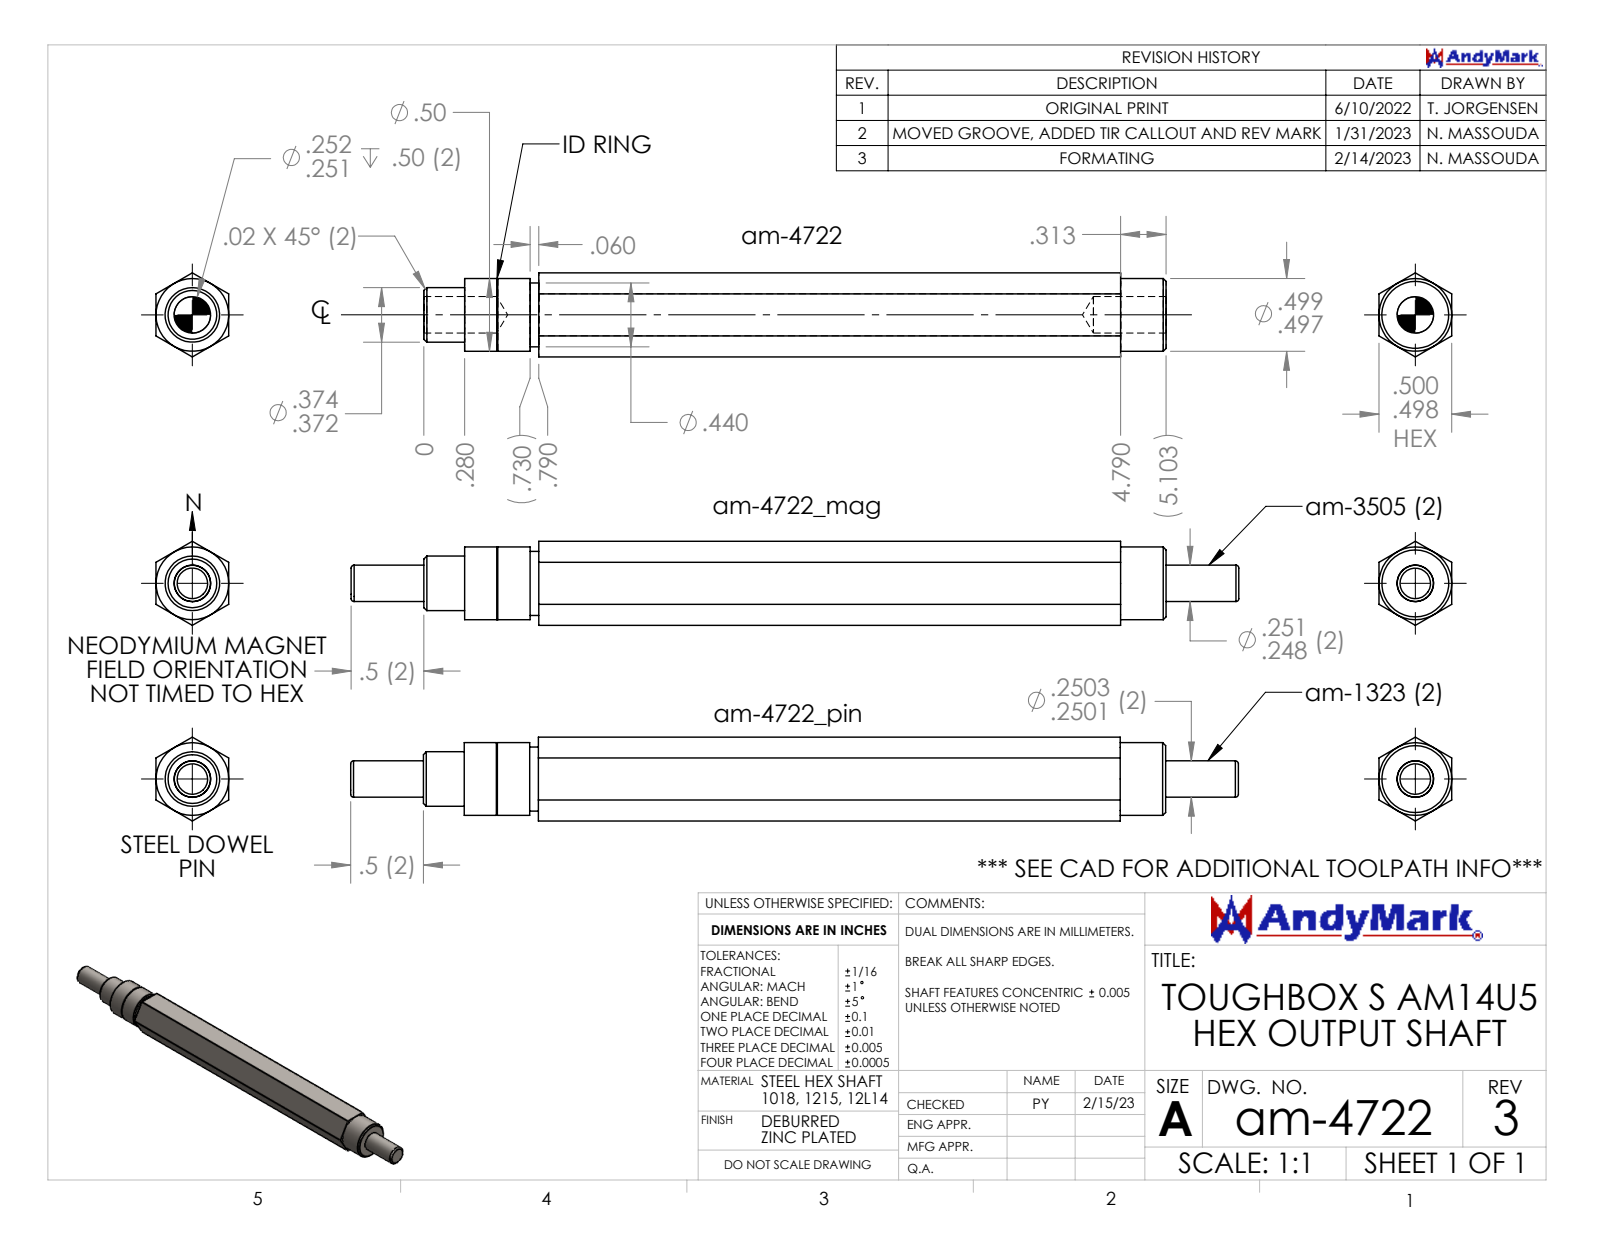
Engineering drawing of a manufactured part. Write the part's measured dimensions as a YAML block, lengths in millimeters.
part_name: "am-4722 ToughBox S AM14U5 Hex Output Shaft"
step_written_by: "SolidWorks 2022 (CONFIG_CONTROL_DESIGN)"
units: millimeters
bodies: {solids: 1, faces: 43, planar: 17, cylindrical: 14, other: 12}
overall_size: [129.6, 14.7, 12.7]
volume: 16440
surface_area: 6347
round_holes:
  - {diameter: 6.4, count: 1}
round_bosses_or_shafts:
  - {diameter: 12.7, count: 1}
  - {diameter: 11.2, count: 1}
  - {diameter: 9.5, count: 1}
face_to_face_distances: [12.7, 122.5, 13, 109.5, 11.4, 1.5, 111, 7.1, 18.5, 20.1]
